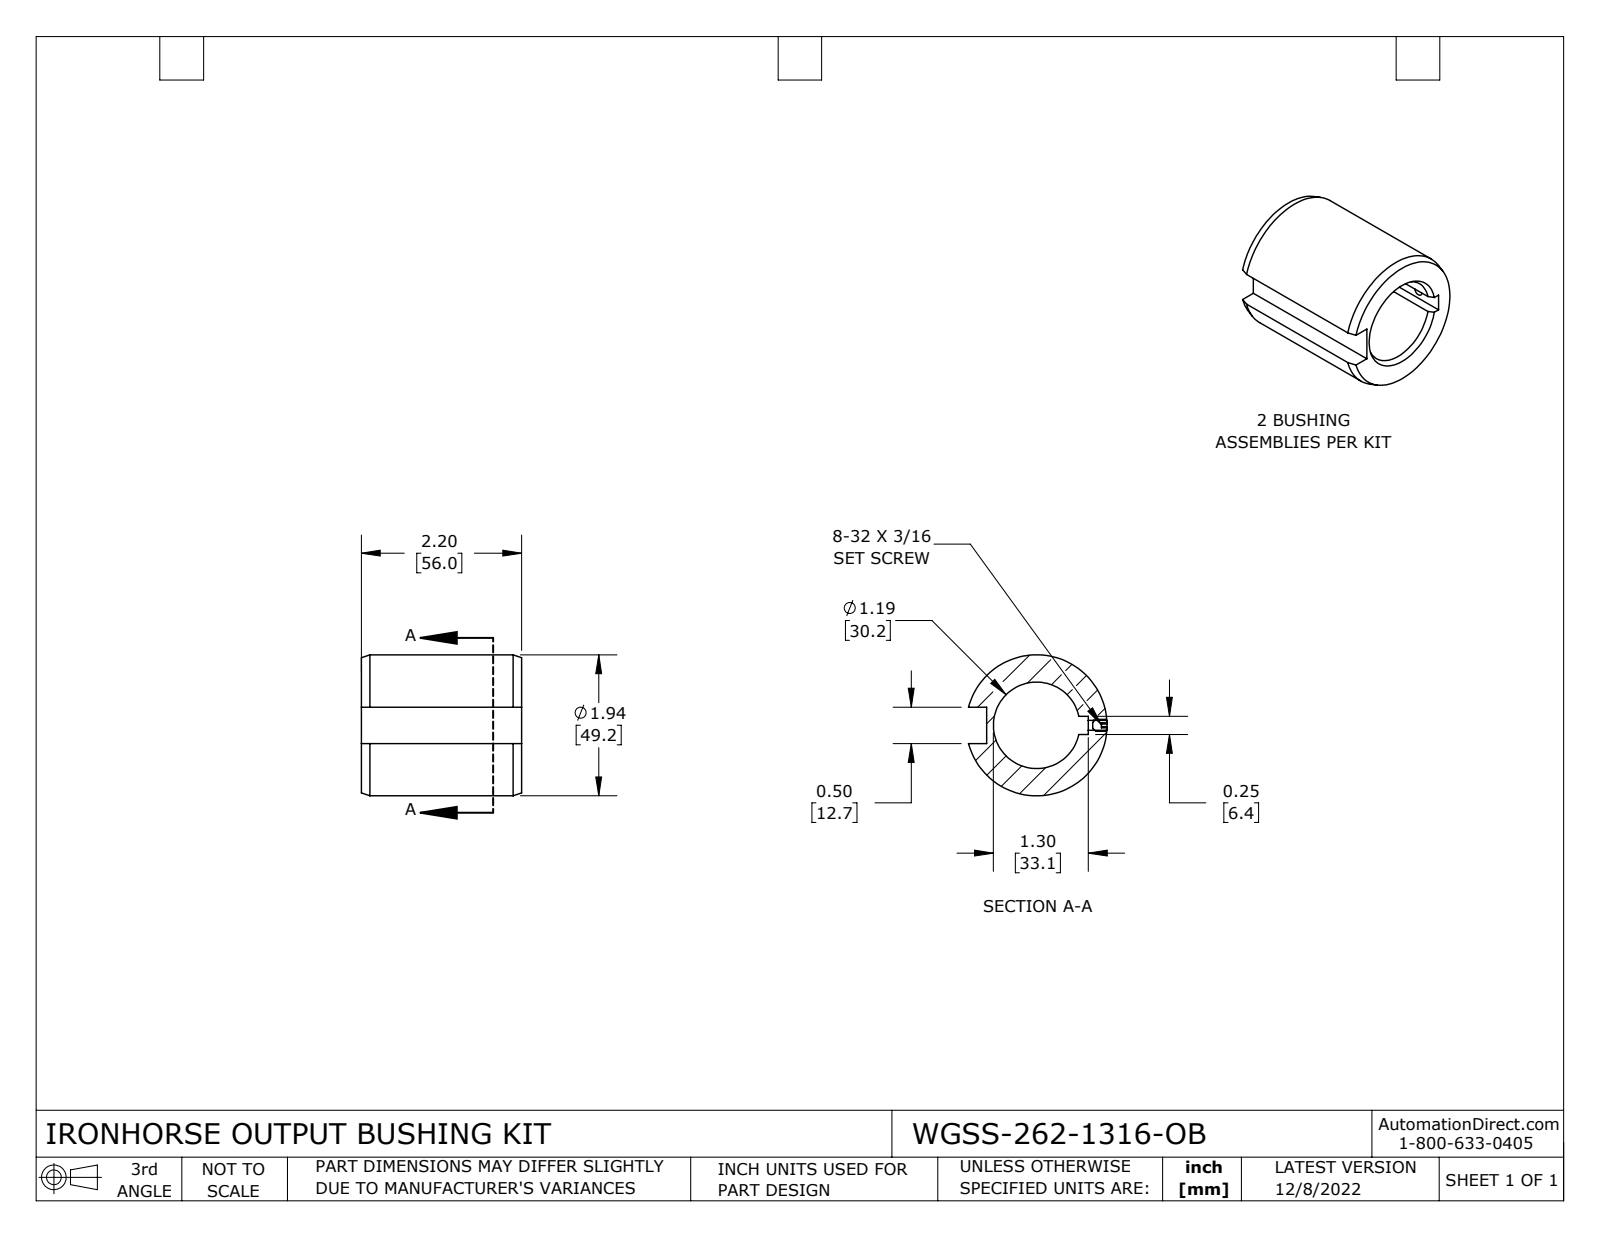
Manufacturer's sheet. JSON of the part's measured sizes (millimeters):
{"part_name": "WGSS-262-1316-OB", "step_written_by": "SolidWorks 2021 (CONFIG_CONTROL_DESIGN)", "units": "millimeters", "bodies": {"solids": 2, "faces": 42, "planar": 17, "cylindrical": 10, "other": 15}, "overall_size": [56, 49.21, 48.38], "volume_mm3": 59864, "surface_area_mm2": 16933, "round_holes": [[3.45, 1], [30.16, 1]], "round_bosses_or_shafts": [[49.21, 1], [4.16, 1]], "face_to_face_distances": [56, 3.18, 9.52, 12.7, 35.47, 6.34, 1.5, 1.56, 37.03, 5]}
